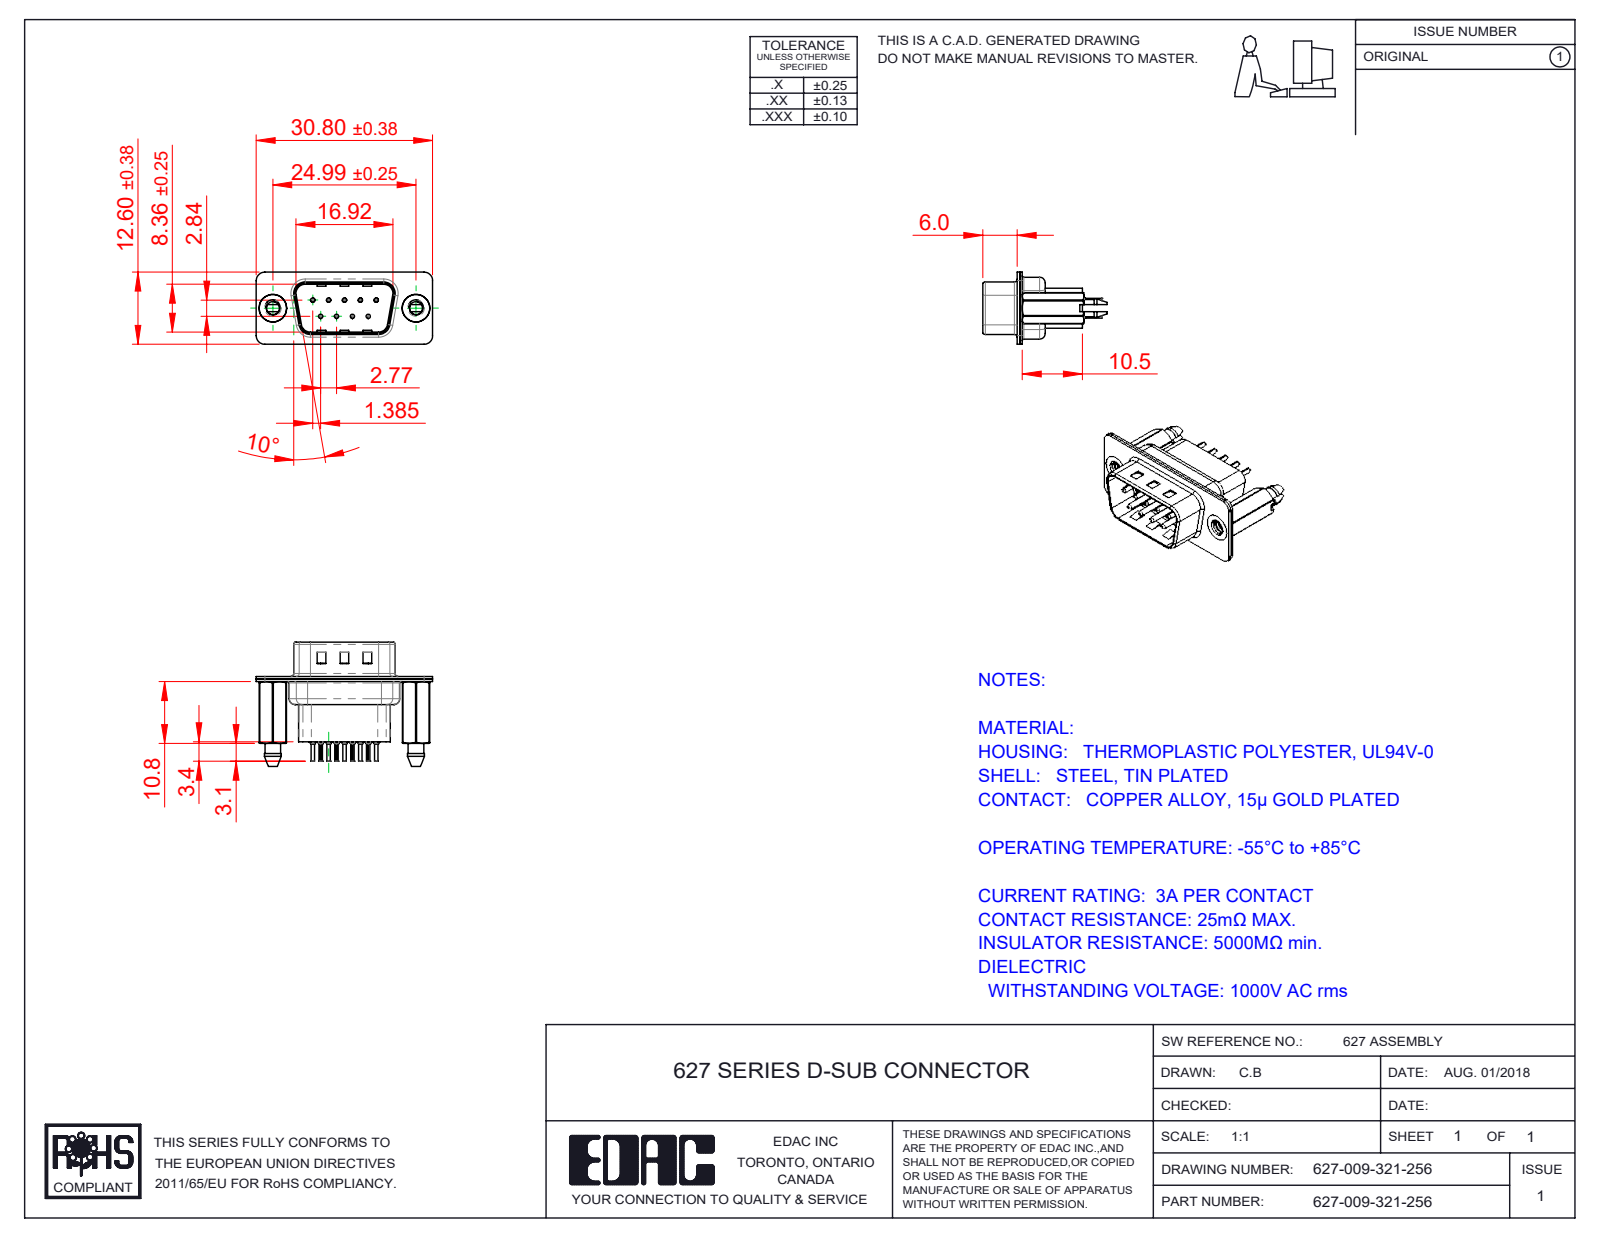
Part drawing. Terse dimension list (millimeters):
name: 627 Contact Row 2_21H; 627-009-321-256; 627 4-40 Threaded Boardlock_HP; 627 Contact Row 1_21H (+3 more)
written by: SolidWorks 2020 (CONFIG_CONTROL_DESIGN)
unit: mm
bodies: 14 solids, 1300 faces (355 planar, 530 cylindrical, 415 other)
size: 30.8 × 21.7 × 12.6
volume: 2 023 mm³; area: 5 281 mm²
holes: 9× ⌀0.2, 9× ⌀0.35, 9× ⌀1.1, 9× ⌀1.6, 2× ⌀2.26, 2× ⌀4, 2× ⌀4.8
bosses: 9× ⌀2, 9× ⌀1.5, 9× ⌀0.75, 9× ⌀0.6, 2× ⌀4.9
rounds: 20× R1.5, 18× R0.1, 12× R2, 10× R1.6, 8× R0.5, 4× R0.25, 4× R0.6, 4× R0.65
face distances: 0.45, 0.4, 0.9, 0.82, 9.58, 1.4, 1.5, 0.68, 7.68, 1.08
hole spacings: 3.16, 2.77, 5.54, 5.03, 5.04, 8.31, 7.48, 7.49
